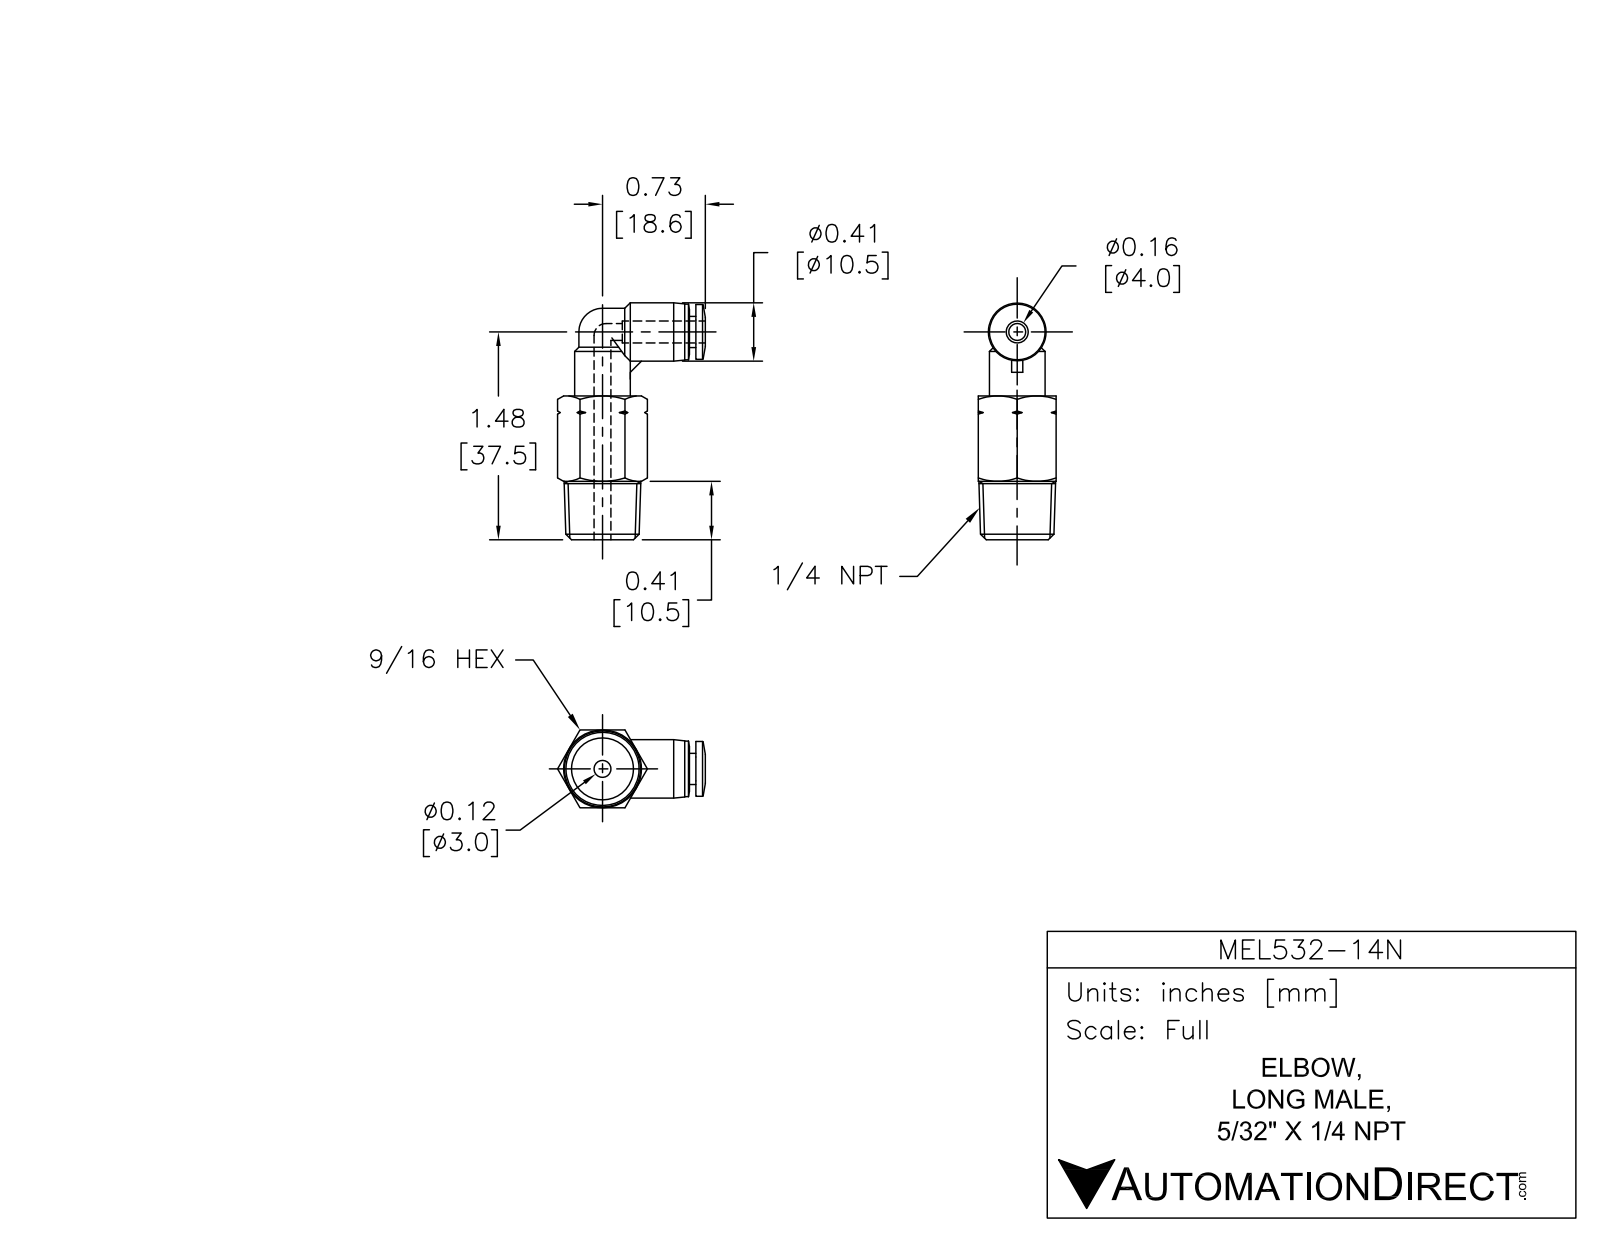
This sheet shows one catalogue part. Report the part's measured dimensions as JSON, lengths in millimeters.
{"part_name": "MEL532-14N", "step_written_by": "SolidWorks 2015 (AUTOMOTIVE_DESIGN)", "units": "millimeters", "bodies": {"solids": 1, "faces": 85, "planar": 16, "cylindrical": 21, "other": 48}, "overall_size": [42.7, 26.6, 14], "volume_mm3": 5750, "surface_area_mm2": 3040, "round_holes": [[3, 2], [4.3, 1]], "round_bosses_or_shafts": [[10, 2], [10.5, 1], [9.9, 1], [5.6, 1]], "partial_cylinders_radius": [[4.2, 2]], "face_to_face_distances": [14, 26, 1.1, 11.9, 13.1, 6, 8, 10.5, 15.5, 2]}
